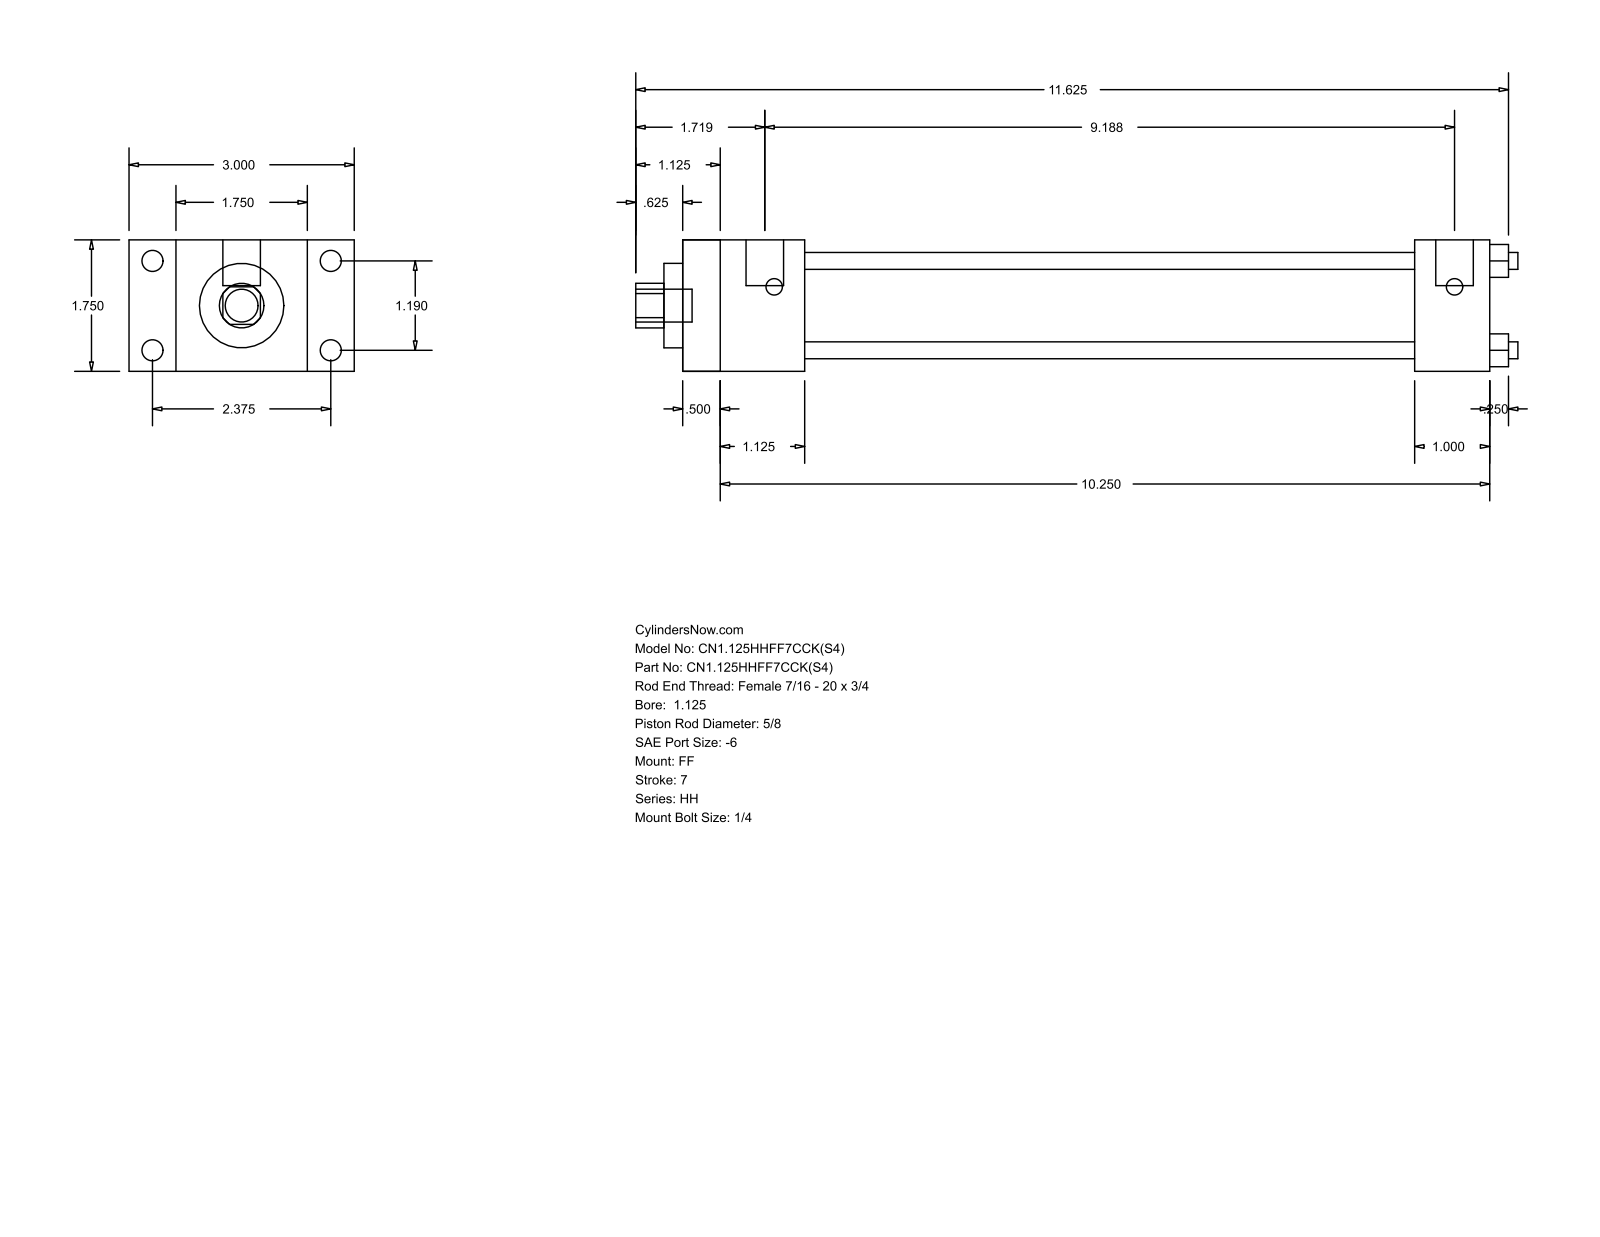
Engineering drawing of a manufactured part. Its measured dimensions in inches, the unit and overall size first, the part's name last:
Units: inches
Overall size (bounding box): 11.75 × 3 × 1.75
Round holes (diameter × count): ⌀0.225 ×4, ⌀0.625 ×1, ⌀1.125 ×1, ⌀1.375 ×1
Round bosses / shafts (diameter × count): ⌀0.281 ×4, ⌀0.219 ×4, ⌀0.5 ×2, ⌀0.437 ×1
Partial cylindrical surfaces — rounded edges, fillets, slot ends (radius × count): R0.297 ×1
Main face-to-face distances: 1.75, 10.75, 0.5, 10.25, 0.625, 2.375, 1.125, 1.625, 9.75, 9.25
Hole centre spacings: 0.841, 1.19, 1.683
Bodies: 0 solids, 92 faces (64 planar, 28 cylindrical, 0 other)
Part name (STEP PRODUCT): HH_FF__0112_0.625
STEP written by: GSSL Pune (CONFIG_CONTROL_DESIGN)
